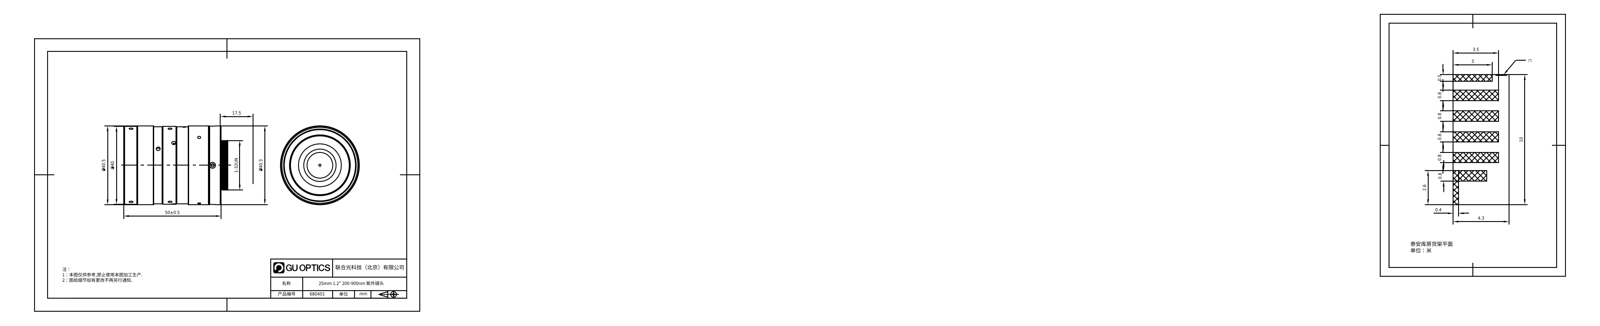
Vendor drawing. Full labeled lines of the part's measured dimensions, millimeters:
Part name (STEP PRODUCT): 680401
STEP written by: SolidWorks 2020 (CONFIG_CONTROL_DESIGN)
Units: millimetres
Bodies: 7 solids, 168 faces (50 planar, 68 cylindrical, 50 other)
Overall size (bounding box): 53.47 × 40.5 × 40.5
Volume: 39 438 mm³ · Surface area: 28 330 mm²
Round holes (diameter × count): ⌀2 ×12, ⌀1.6 ×7, ⌀3 ×6, ⌀1.4 ×3, ⌀13.2 ×1, ⌀15 ×1, ⌀15.2 ×1, ⌀16.6 ×1, ⌀19.6 ×1, ⌀22 ×1, ⌀22.4 ×1, ⌀30.4 ×1
Round bosses / shafts (diameter × count): ⌀40.5 ×1, ⌀40.3 ×1, ⌀40 ×1, ⌀39.4 ×1, ⌀36.9 ×1, ⌀36.7 ×1, ⌀34.6 ×1, ⌀34.1 ×1
Main face-to-face distances: 44.16, 30.02, 14.14, 0.56, 47.97, 3.25, 17.39, 47.41, 3.81, 17.95
Hole centre spacings: 17.49, 24.74, 17, 29.44, 8.94, 17.25, 20, 24.39
